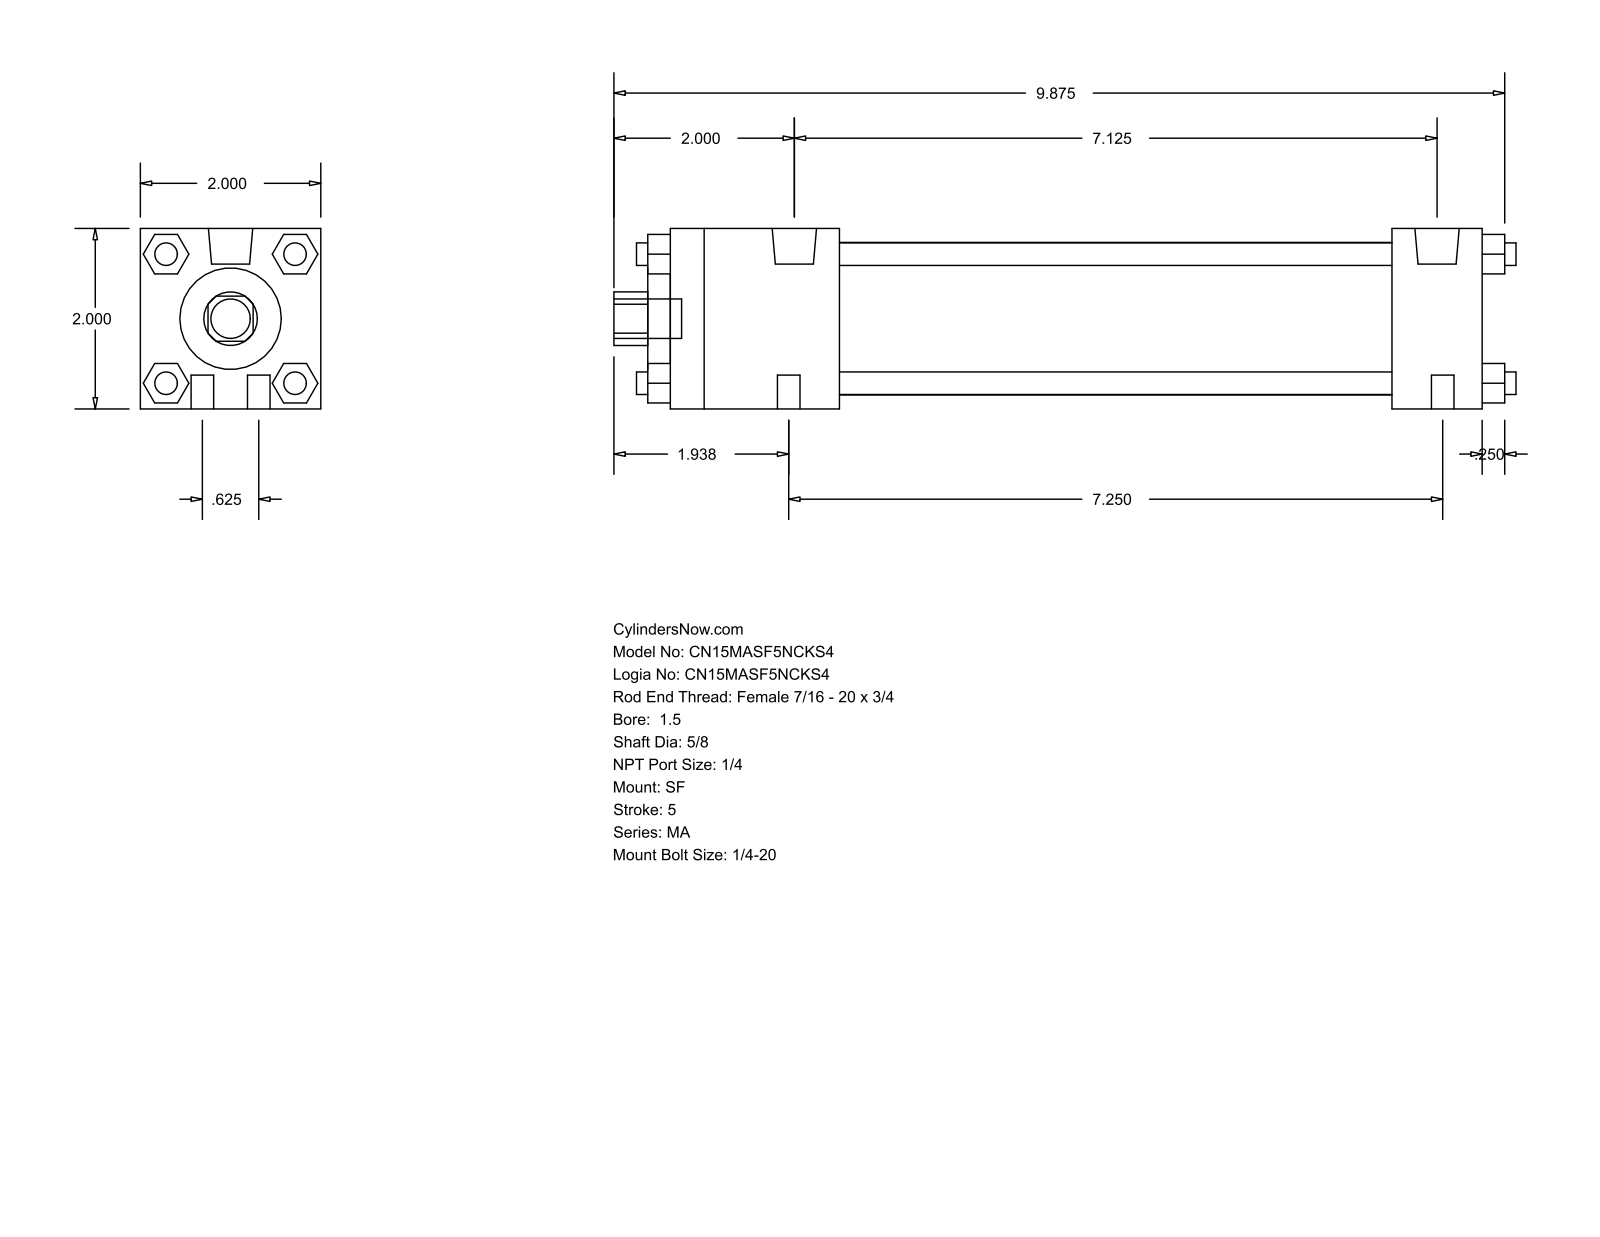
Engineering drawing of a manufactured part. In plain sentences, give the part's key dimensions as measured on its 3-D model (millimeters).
The part is named "MA_SF__0150_0.625". Its 3-D file was written by "GSSL Pune (CONFIG_CONTROL_DESIGN)". It is 0 solids with 124 faces: 94 planar, 30 cylindrical and 0 other. Overall it measures 254 by 50.8 by 50.8 millimeters. Round holes: 1 of diameter 15.88, 1 of diameter 28.57, 1 of diameter 42.93. Round bosses or shafts: 8 of diameter 6.35, 2 of diameter 12.49, 2 of diameter 7.94, 1 of diameter 11.11. Partial cylindrical surfaces (rounded edges, fillets, slot ends): 1 of radius 7.54. The main face-to-face distances are 50.8, 228.59, 6.35, 234.94, 47.62, 203.19, 155.57, 180.97, 25.4, 53.97.
